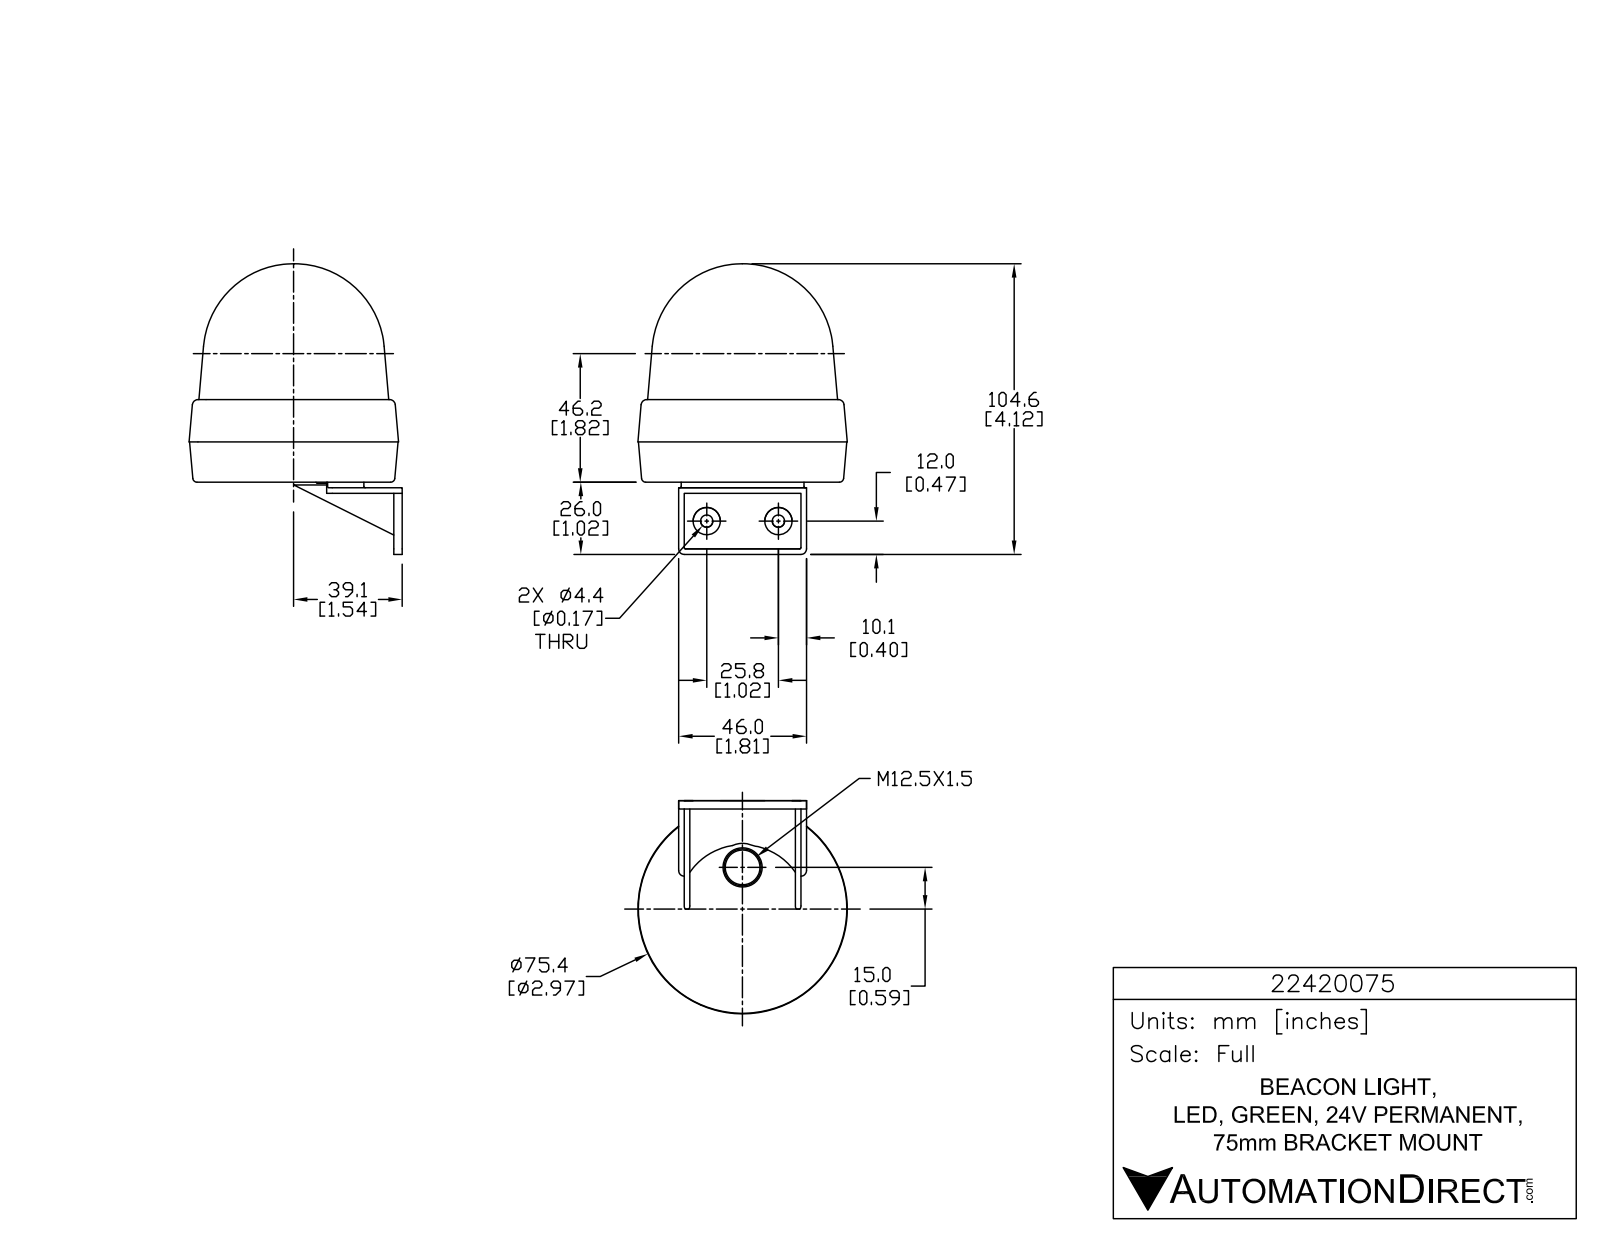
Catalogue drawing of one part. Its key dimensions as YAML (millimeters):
part_name: "22420075"
step_written_by: "SolidWorks 2015 (AUTOMOTIVE_DESIGN)"
units: millimeters
bodies: {solids: 1, faces: 819, planar: 549, cylindrical: 180, other: 90}
overall_size: [104.6, 82.6, 75.4]
volume: 262500
surface_area: 27080
round_holes:
  - {diameter: 1.5, count: 3}
  - {diameter: 4.4, count: 2}
round_bosses_or_shafts:
  - {diameter: 8.6, count: 3}
  - {diameter: 2.1, count: 3}
  - {diameter: 9.8, count: 2}
partial_cylinders:
  - {radius: 0.1, count: 9}
  - {radius: 0.1, count: 6}
  - {radius: 0.3, count: 6}
  - {radius: 0.3, count: 6}
  - {radius: 0.3, count: 6}
  - {radius: 0.5, count: 6}
  - {radius: 5, count: 6}
  - {radius: 2, count: 4}
face_to_face_distances: [2, 4, 40, 1, 3, 42, 38, 2, 42, 44]
hole_center_spacings: [25.8]
